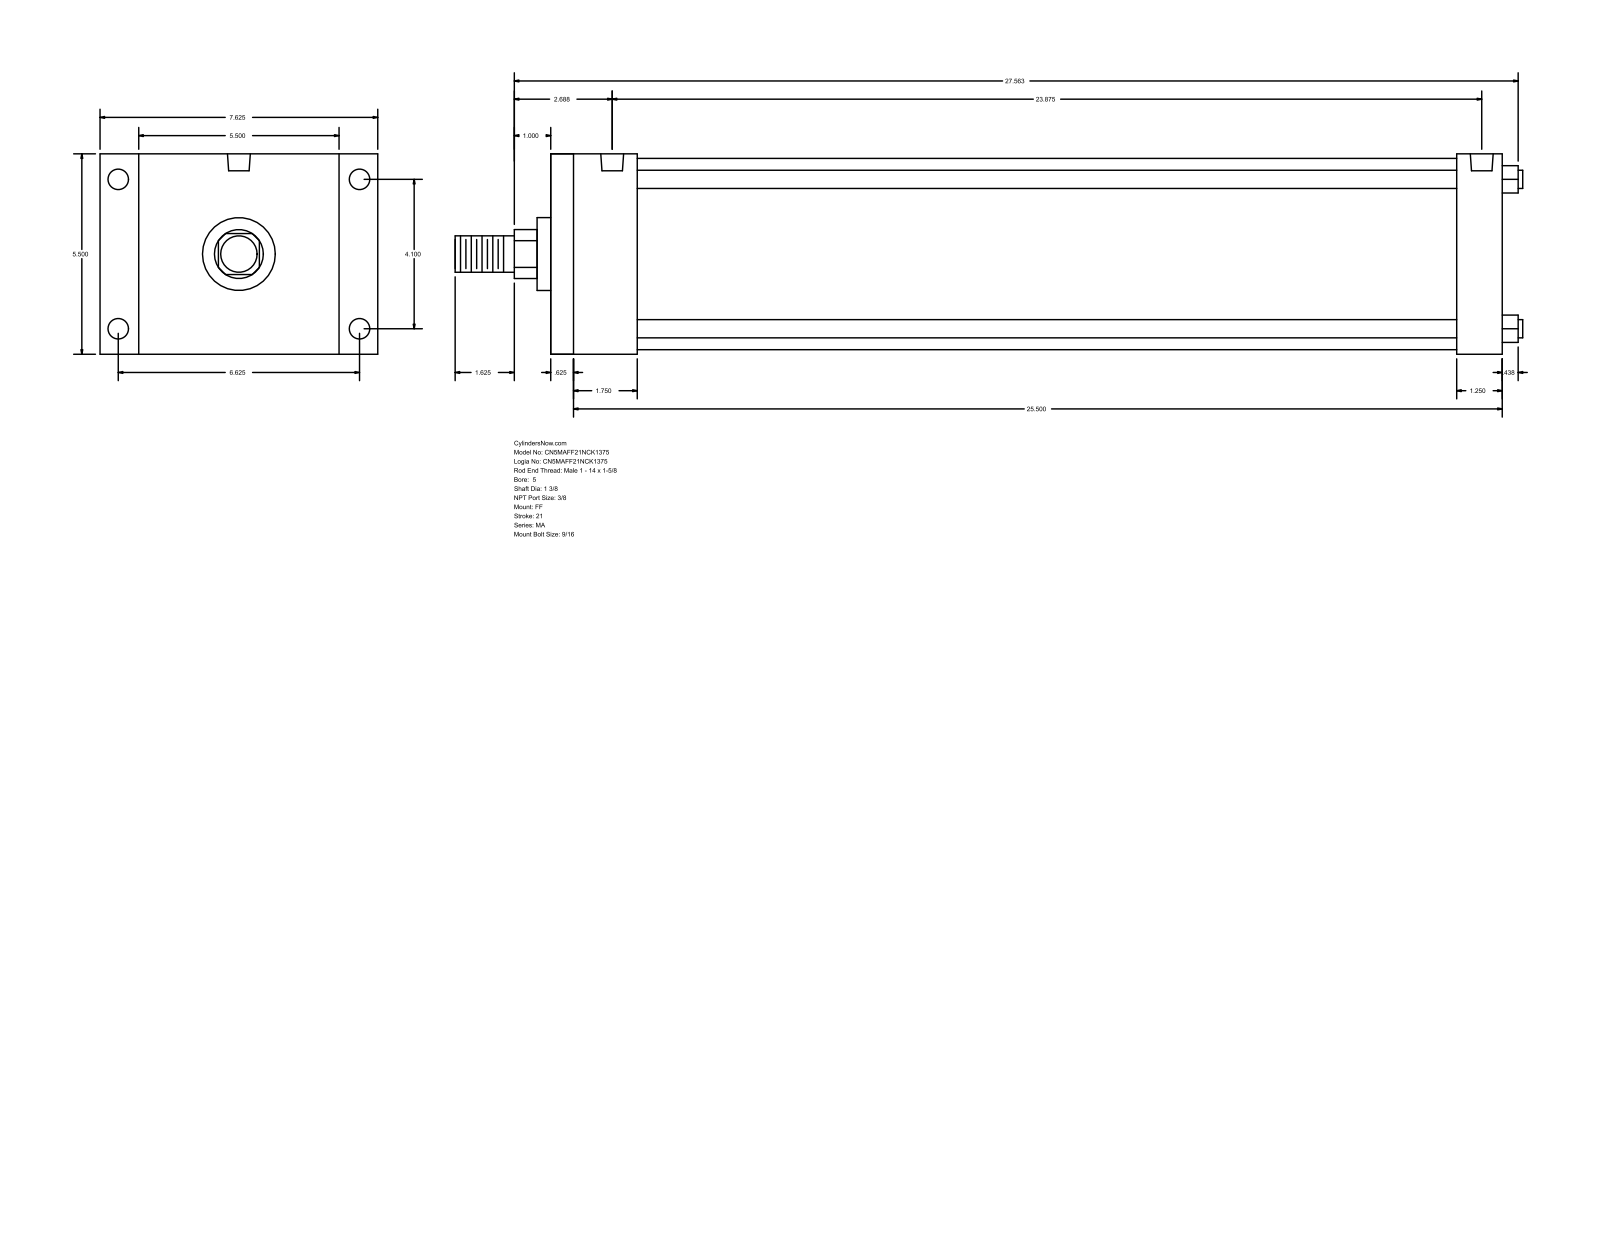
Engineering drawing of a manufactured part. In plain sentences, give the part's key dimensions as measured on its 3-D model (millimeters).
The part is named "MA_FF__0500_1.375". Its 3-D file was written by "GSSL Pune (CONFIG_CONTROL_DESIGN)". It is 0 solids with 92 faces: 64 planar, 28 cylindrical and 0 other. Overall it measures 744.54 by 193.68 by 139.7 millimeters. Round holes: 4 of diameter 11.11, 4 of diameter 14.29, 2 of diameter 15.93. Round bosses or shafts: 4 of diameter 12.7, 1 of diameter 133.35, 1 of diameter 50.8, 1 of diameter 34.92, 1 of diameter 25.4. Partial cylindrical surfaces (rounded edges, fillets, slot ends): 1 of radius 17.06. The main face-to-face distances are 139.7, 663.58, 15.87, 647.71, 631.83, 615.96, 31.75, 60.32, 44.45, 571.51. The hole center spacings are 4.77, 104.14, 168.28, 197.9, 596.89, 601.66, 606.43.
